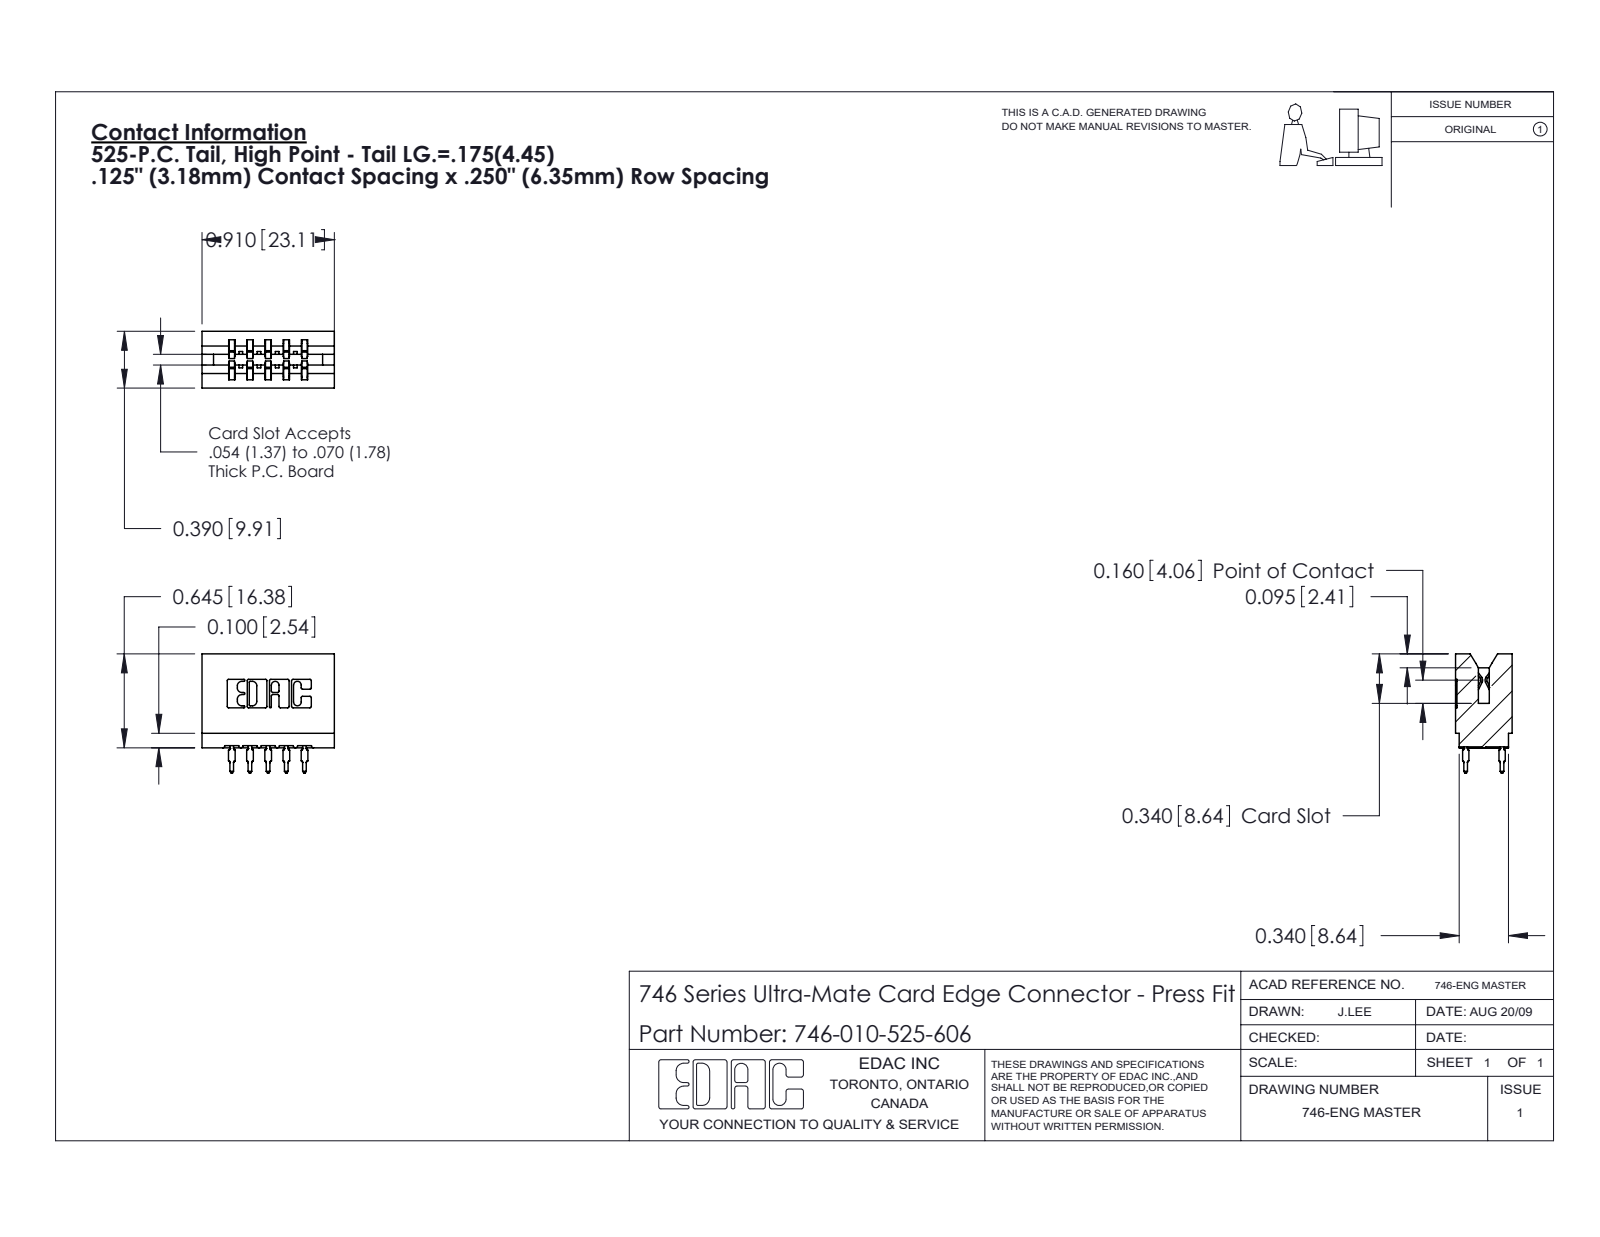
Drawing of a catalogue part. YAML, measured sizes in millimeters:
part_name: "746 Part_.340 Slot Depth - 06; 746-010-525-606; 746-292-001_525"
step_written_by: "SolidWorks 2020 (CONFIG_CONTROL_DESIGN)"
units: millimeters
bodies: {solids: 11, faces: 993, planar: 516, cylindrical: 217, other: 260}
overall_size: [23.1, 20.8, 9.9]
volume: 2830
surface_area: 3475
partial_cylinders:
  - {radius: 0.3, count: 22}
  - {radius: 0.5, count: 20}
  - {radius: 0.1, count: 8}
  - {radius: 0.3, count: 8}
  - {radius: 0.2, count: 6}
  - {radius: 0.4, count: 6}
  - {radius: 0.8, count: 6}
  - {radius: 0.7, count: 3}
face_to_face_distances: [6.4, 1.1, 1.4, 8.5, 3.2, 3.2, 9.9, 2.1, 7.4, 5.3]
